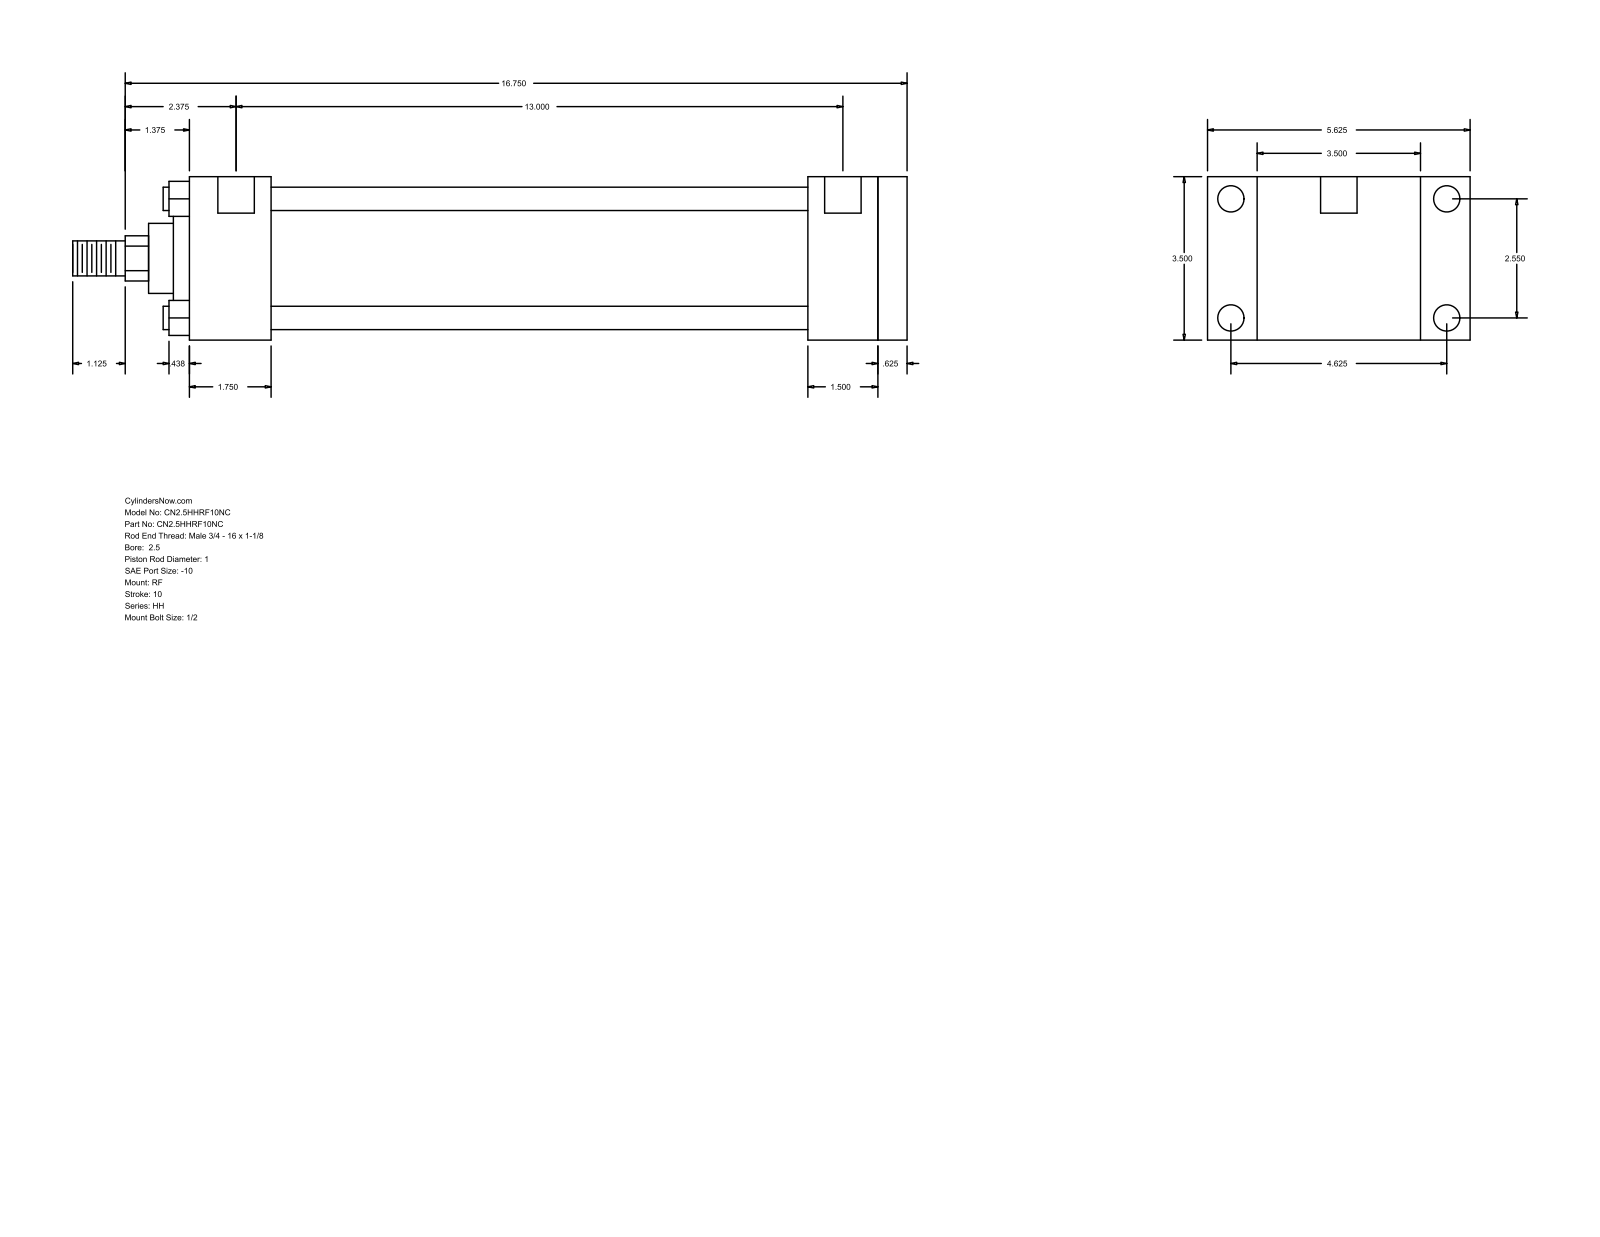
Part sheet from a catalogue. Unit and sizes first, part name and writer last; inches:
Units: inches
Overall size (bounding box): 17.875 × 5.625 × 3.5
Round holes (diameter × count): ⌀0.219 ×4, ⌀0.563 ×4, ⌀0.781 ×2
Round bosses / shafts (diameter × count): ⌀0.5 ×4, ⌀2.875 ×1, ⌀2.375 ×1, ⌀1.5 ×1, ⌀1 ×1, ⌀0.75 ×1
Partial cylindrical surfaces — rounded edges, fillets, slot ends (radius × count): R0.484 ×1
Main face-to-face distances: 3.5, 0.625, 14.75, 15.375, 1.75, 13, 13.625, 13.25, 11.5, 1.5
Hole centre spacings: 0.063, 2.55, 4.625, 5.281, 13.062, 13.125, 13
Bodies: 0 solids, 94 faces (65 planar, 29 cylindrical, 0 other)
Part name (STEP PRODUCT): HH_RF__0250_1
STEP written by: GSSL Pune (CONFIG_CONTROL_DESIGN)
